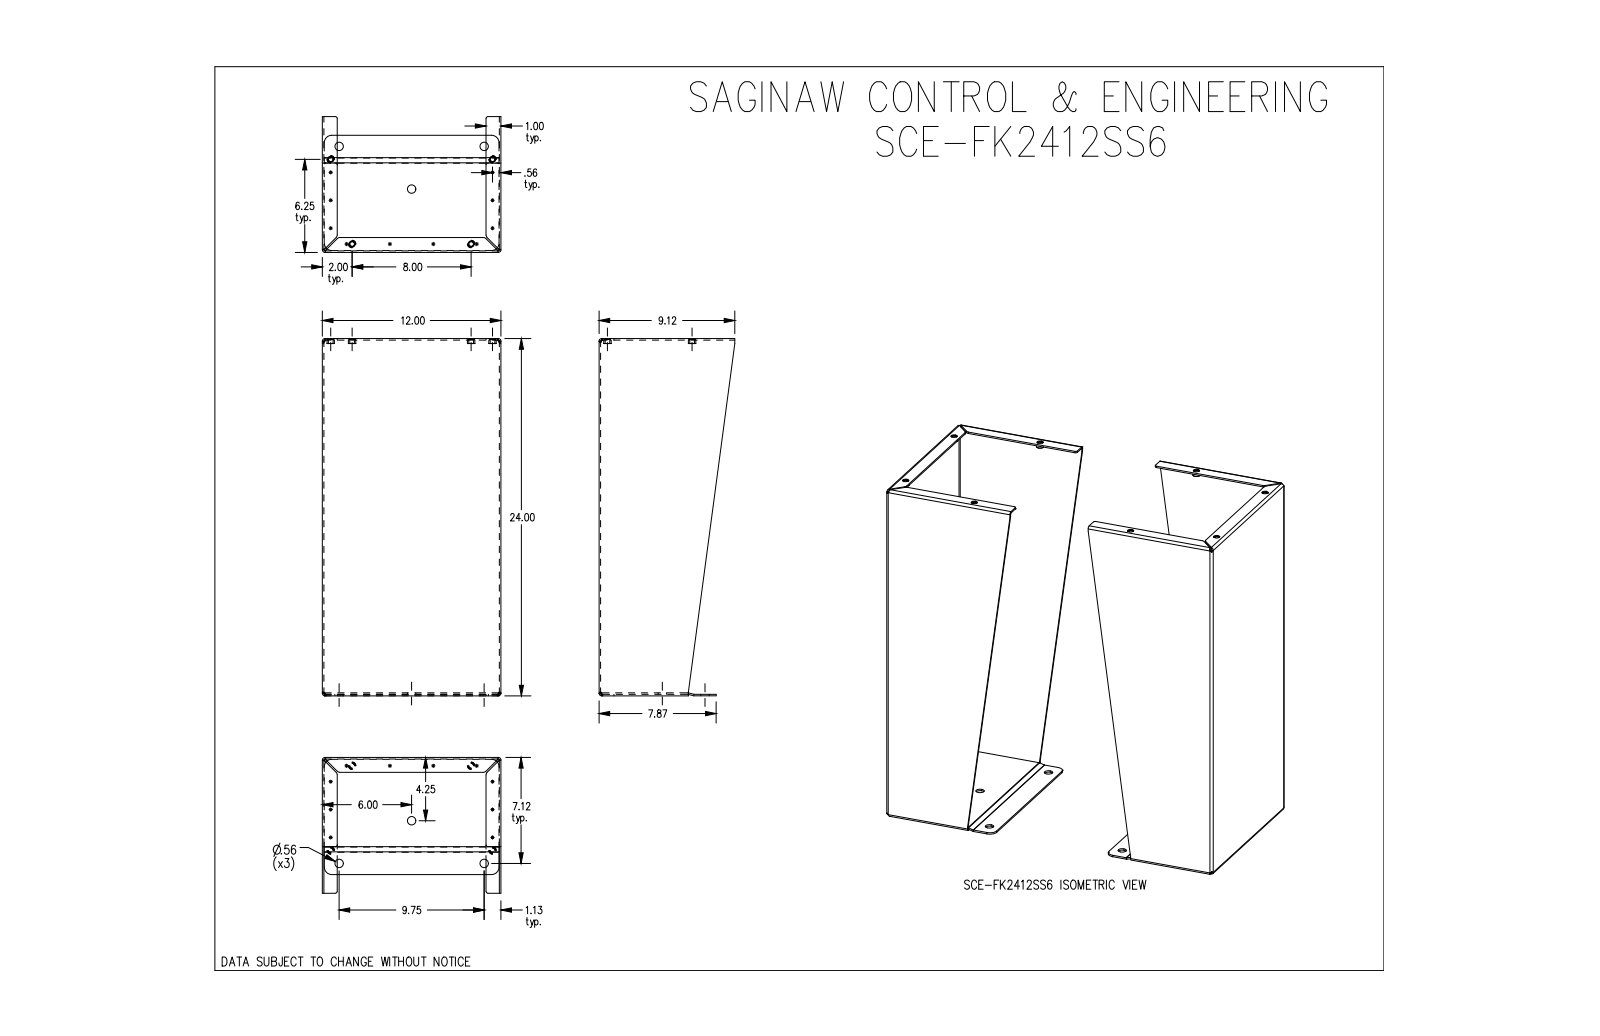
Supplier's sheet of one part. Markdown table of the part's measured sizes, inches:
| quantity | value |
| --- | --- |
| part name | SCE-FK2412SS6 |
| STEP written by | SolidWorks 2019 (CONFIG_CONTROL_DESIGN) |
| units | inches |
| bodies | 12 solids, 286 faces (120 planar, 110 cylindrical, 56 other) |
| overall size | 24 × 24 × 12 |
| volume | 161.4 in³ |
| surface area | 3 140 in² |
| round holes (diameter × count) | 0.312 × 8, 0.413 × 8, 0.563 × 6 |
| round bosses / shafts (diameter × count) | 0.5 × 8, 0.412 × 8 |
| partial cylindrical surfaces (radius × count) | 0.166 × 16, 0.062 × 14, 0.125 × 8, 0.22 × 8, 0.5 × 8, 0.063 × 2 |
| main face-to-face distances | 0.104, 11.896, 23.896, 23.792, 12, 11.792, 24, 0.101, 23.893, 23.688 |
| hole center spacings | 1.035, 5.441, 5.656, 5.793, 5.866, 6.614, 10.646, 11.019 |
